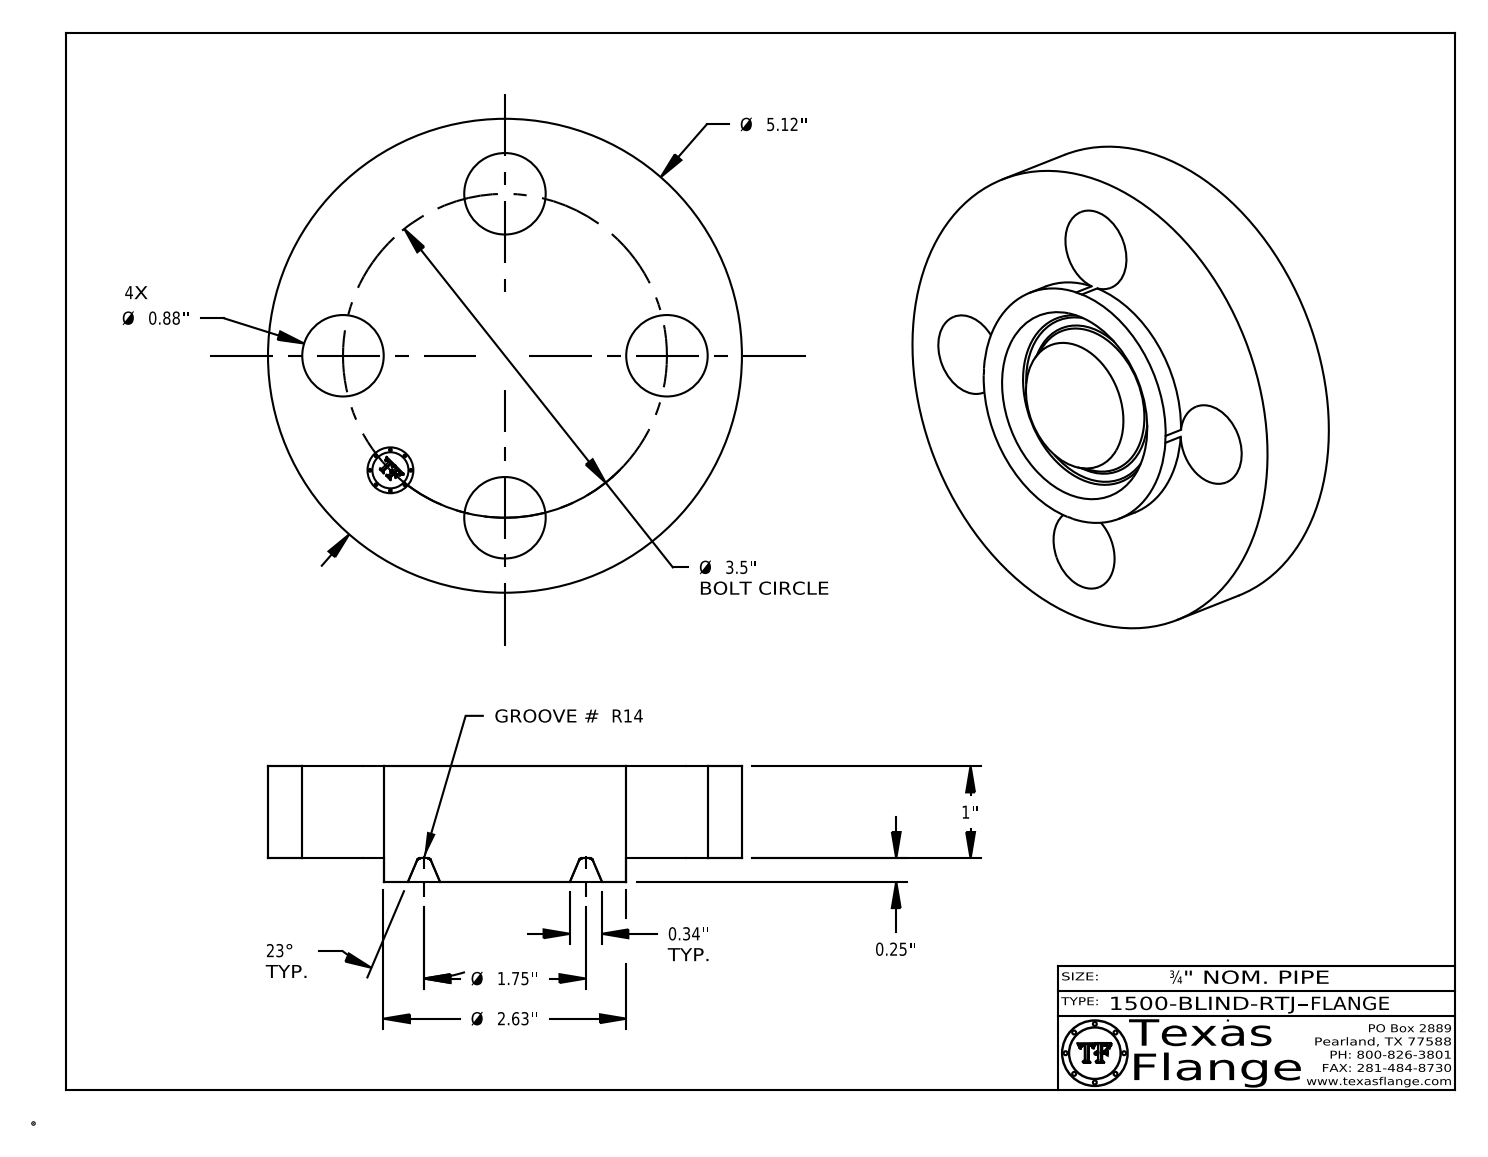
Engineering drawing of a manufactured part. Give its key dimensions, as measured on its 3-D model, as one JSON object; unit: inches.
{"part_name": "1500-BLIND-RTJ", "step_written_by": "CATIA V5 STEP AP214 (AUTOMOTIVE_DESIGN)", "units": "inches", "bodies": {"solids": 1, "faces": 414, "planar": 370, "cylindrical": 36, "other": 8}, "overall_size": [5.12, 5.12, 1.25], "volume_in3": 19.18, "surface_area_in2": 67.38, "round_holes": [[0.88, 4], [0.495, 1]], "round_bosses_or_shafts": [[0.03, 8], [5.12, 1], [2.625, 1], [0.39, 1]], "face_to_face_distances": [1, 0.25, 1.25, 0.015, 1.235, 0.985, 0.148, 0.145, 0.027, 0.096], "hole_center_spacings": [2.475, 1.339, 3.233, 3.5]}
